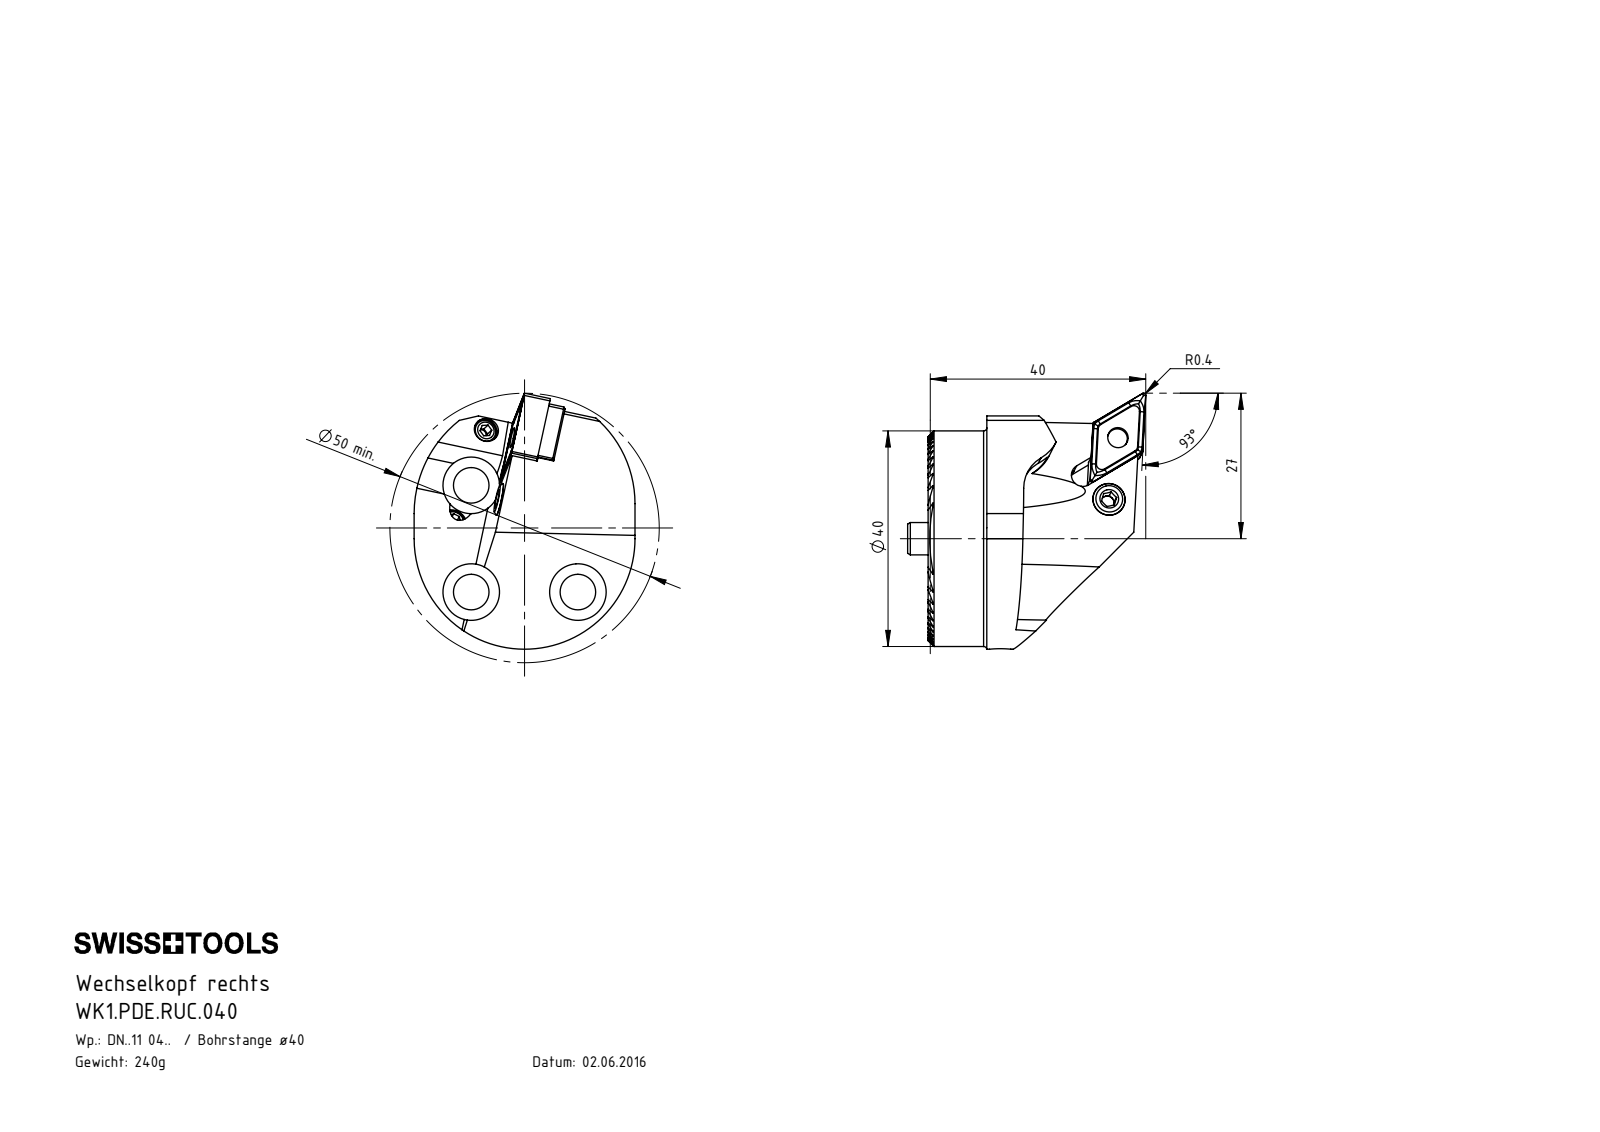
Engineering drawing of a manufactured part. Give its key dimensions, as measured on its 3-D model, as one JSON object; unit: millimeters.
{"part_name": "WDE-ER1.101.000; WK2-ER1.001.012_A_Fertigbearbeitung; WDE-ER3.101.000_A; WKX-ER1.004.005_A_PreviewCfg (+6 more)", "step_written_by": "SolidWorks 2017 (AUTOMOTIVE_DESIGN)", "units": "millimeters", "bodies": {"solids": 15, "faces": 507, "planar": 280, "cylindrical": 118, "other": 109}, "overall_size": [47.5, 44.21, 41], "volume_mm3": 31043, "surface_area_mm2": 13736, "round_holes": [[3.3, 5], [3, 3], [6.6, 3], [10.5, 3], [1.7, 2], [4, 2], [4.5, 2], [3.81, 1], [4.2, 1], [4.8, 1], [5, 1], [6.4, 1]], "round_bosses_or_shafts": [[4, 5], [6, 2], [40, 1], [5.9, 1], [2.87, 1]], "partial_cylinders_radius": [[0.12, 26], [0.4, 8], [2.1, 5], [7, 2], [1.83, 1], [1.85, 1], [2.25, 1], [2.35, 1]], "face_to_face_distances": [1.3, 2.6, 3.9, 12.99, 5.2, 11.69, 9.09, 10.39, 7.79, 6.5], "hole_center_spacings": [14, 19.8, 11.8, 28]}
